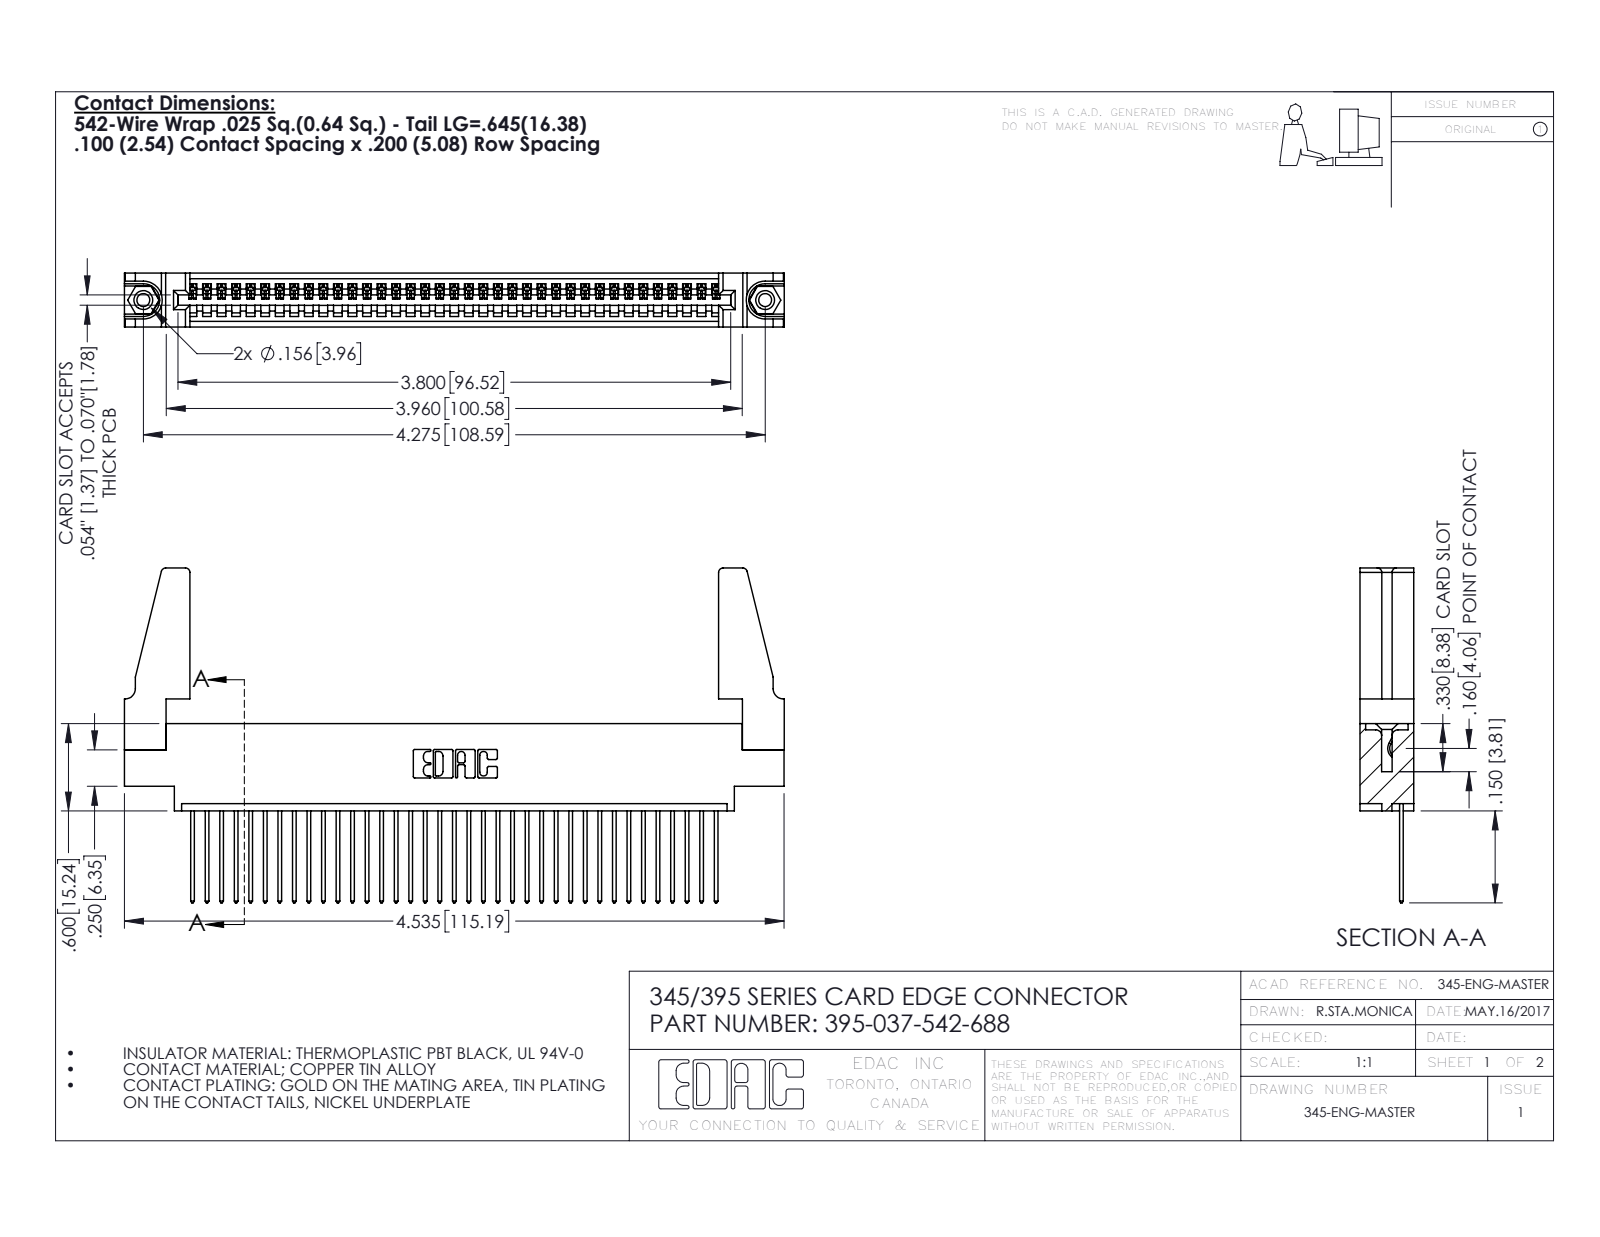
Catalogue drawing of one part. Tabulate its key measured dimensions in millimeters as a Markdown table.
| quantity | value |
| --- | --- |
| part name | 345 Part_0.170 Offset - 0.156 Dia-TH; 345-250-001_345-250-001-102; 345-292-001_345-293-142; 345-220-078_345-220-088 (+1 more) |
| STEP written by | SolidWorks 2016 (CONFIG_CONTROL_DESIGN) |
| units | millimeters |
| bodies | 42 solids, 2400 faces (1636 planar, 748 cylindrical, 16 other) |
| overall size | 115.2 × 58.5 × 9.4 |
| volume | 14 100 mm³ |
| surface area | 18 150 mm² |
| round holes (diameter × count) | 2.3 × 2, 3.2 × 2, 4 × 2, 1.6 × 1 |
| round bosses / shafts (diameter × count) | 3.9 × 2 |
| partial cylindrical surfaces (radius × count) | 0.2 × 74, 0.3 × 74, 0.3 × 22, 0.8 × 8, 0.2 × 6, 0.8 × 6, 0.7 × 3, 0.8 × 2 |
| main face-to-face distances | 1.8, 7.6, 9.4, 2.5, 6.9, 0.6, 5.1, 5.7, 4.4, 3.8 |
| hole center spacings | 6.9, 102.6, 108.6 |
